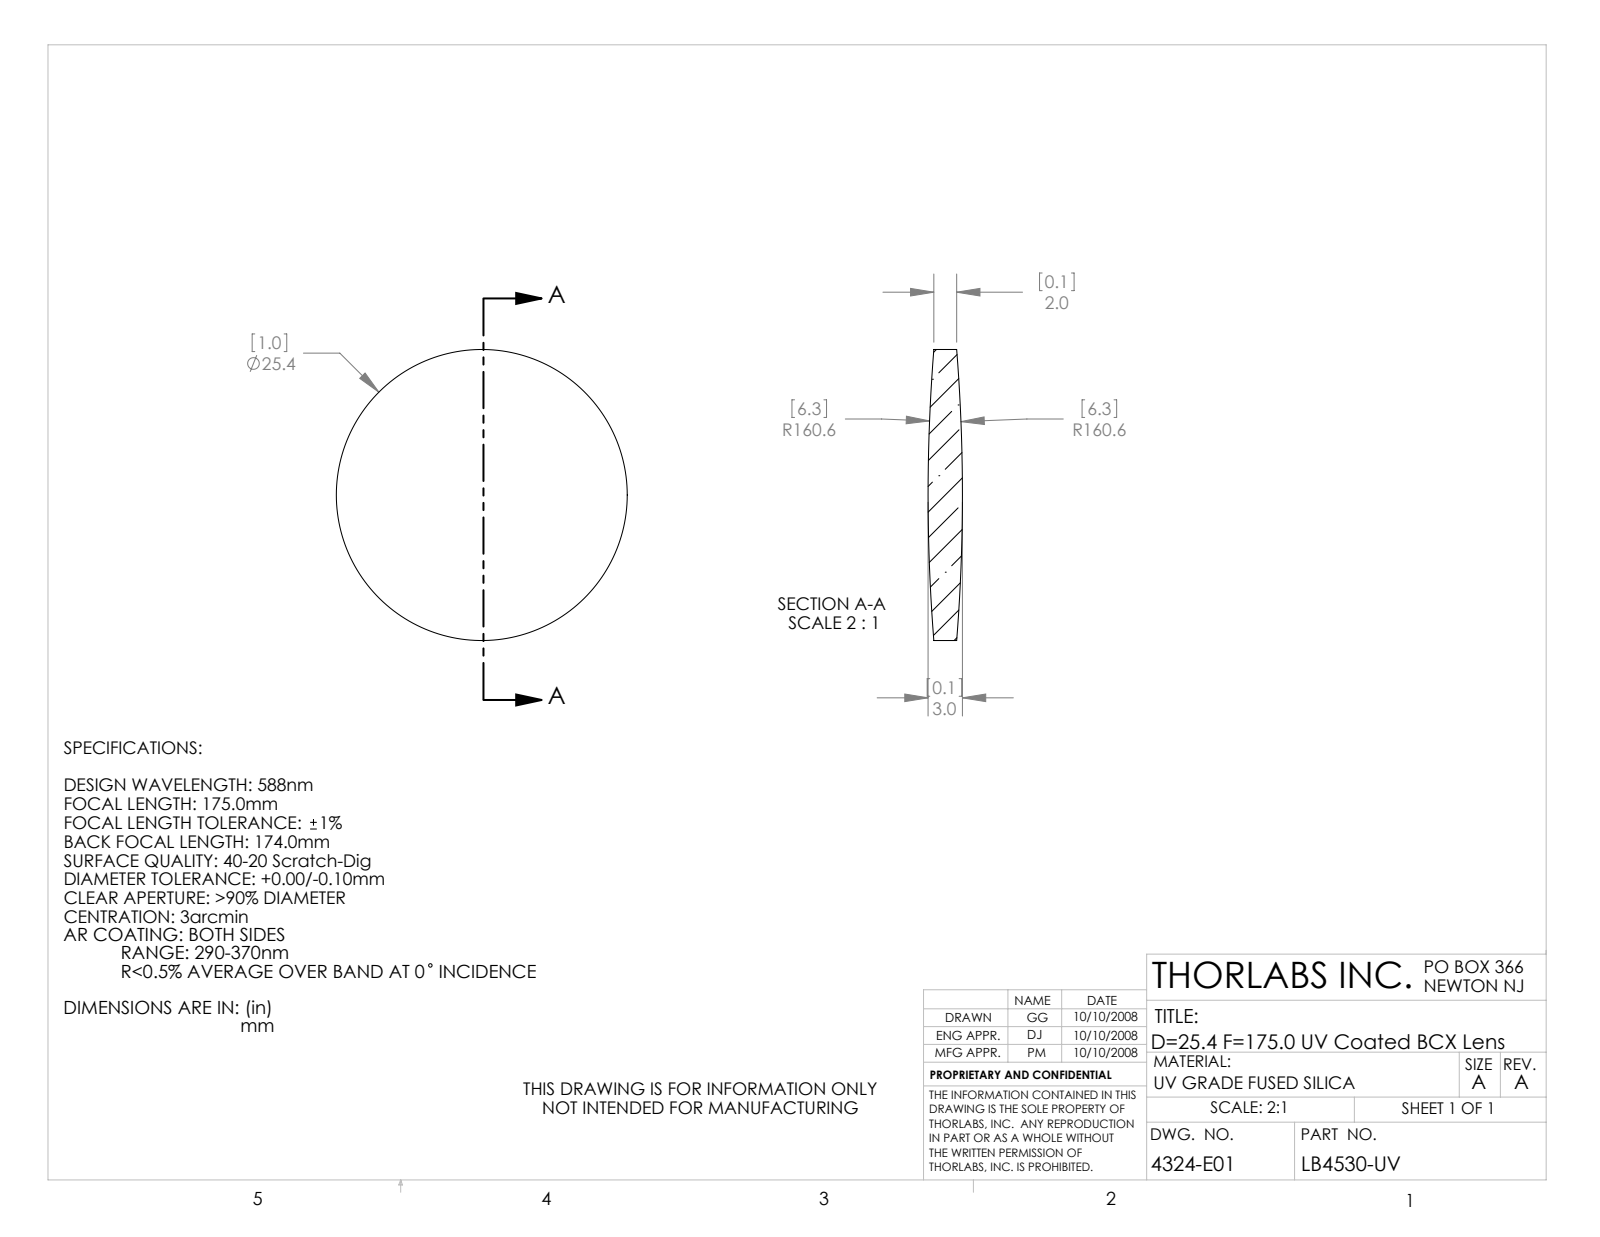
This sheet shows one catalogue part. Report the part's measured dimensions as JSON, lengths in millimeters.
{"part_name": "4324-E0W", "step_written_by": "SolidWorks 2007 (CONFIG_CONTROL_DESIGN)", "units": "millimeters", "bodies": {"solids": 1, "faces": 6, "planar": 0, "cylindrical": 2, "other": 4}, "overall_size": [25.4, 25.4, 3], "volume_mm3": 1265, "surface_area_mm2": 1174, "round_bosses_or_shafts": [[25.4, 1]]}
